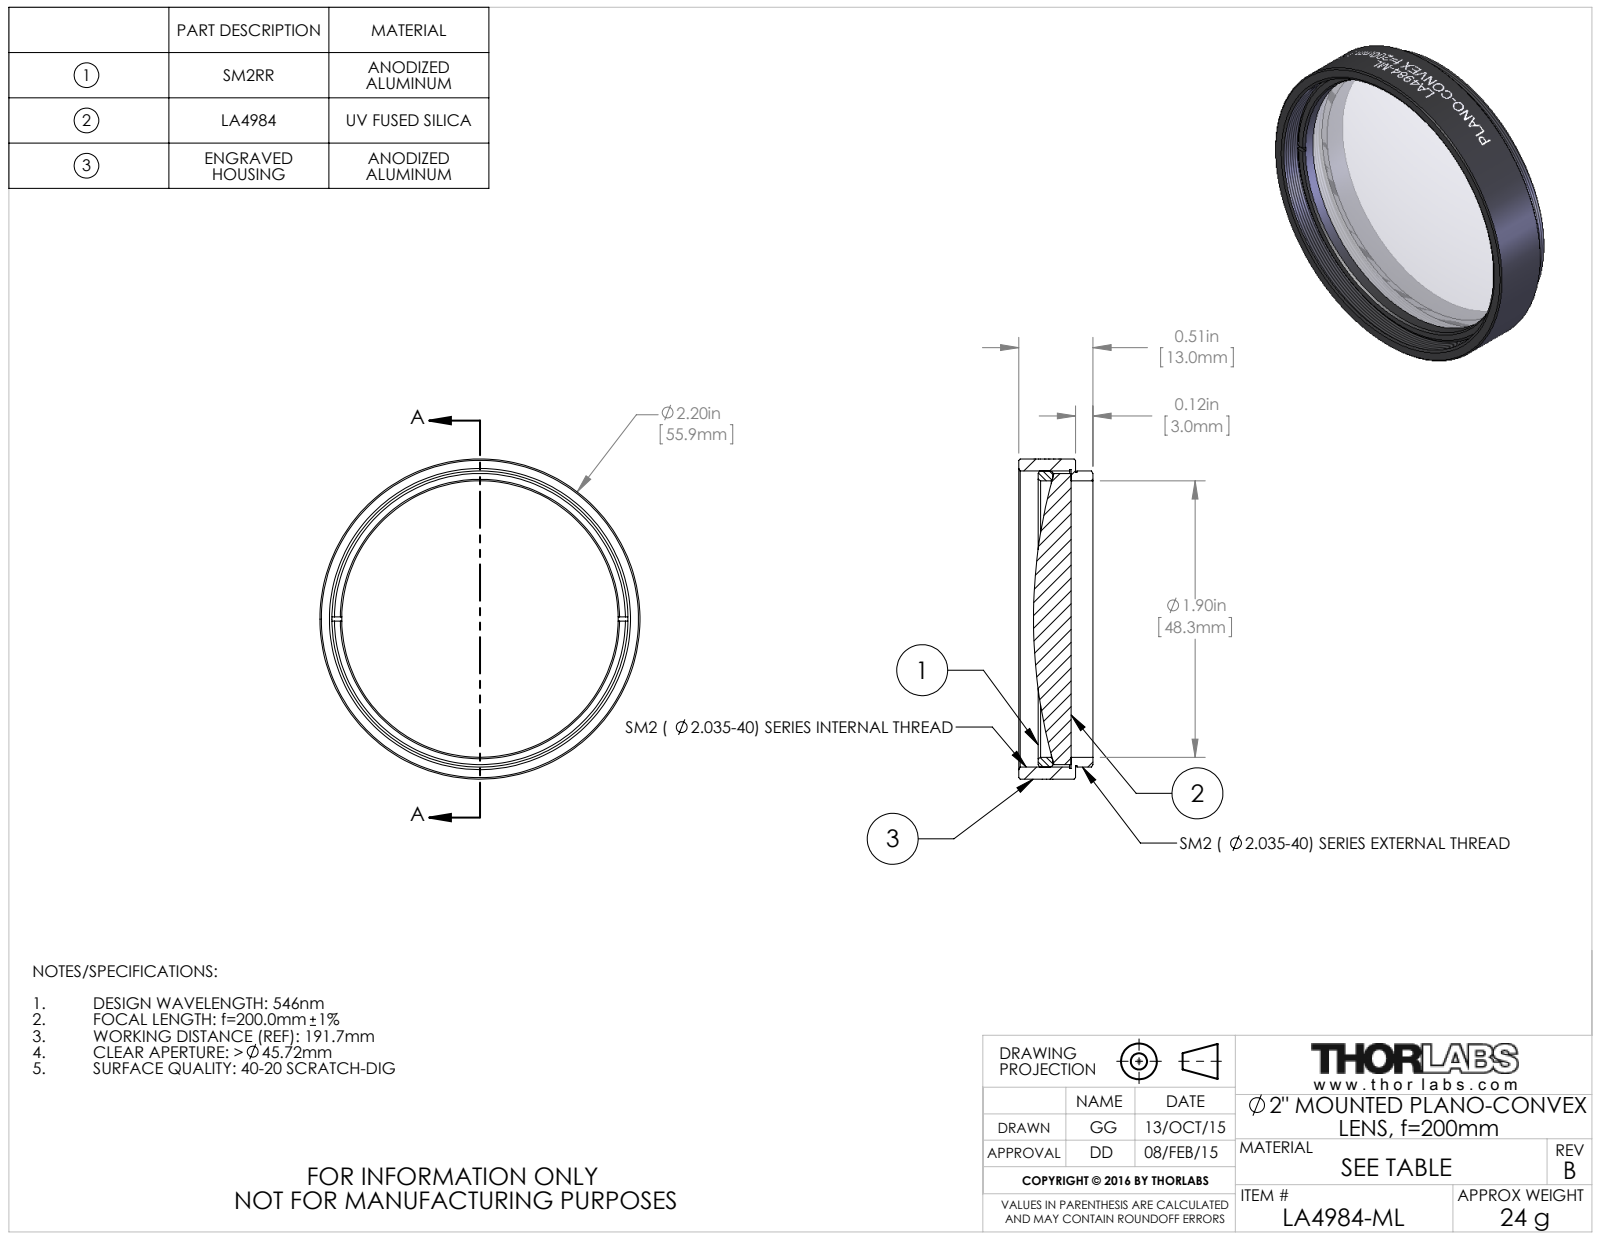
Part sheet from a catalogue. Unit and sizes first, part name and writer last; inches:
Units: inches
Overall size (bounding box): 2.2 × 2.2 × 0.51
Round holes (diameter × count): ⌀1.9 ×1, ⌀2.055 ×1
Round bosses / shafts (diameter × count): ⌀2.2 ×1, ⌀2.035 ×1, ⌀2.015 ×1, ⌀2 ×1
Main face-to-face distances: 0.03, 0.39, 0.36, 0.12, 0.15, 0.51, 0.278, 0.157, 0.128, 0.233
Volume: 0.907 in³ · Surface area: 17.65 in²
Bodies: 3 solids, 112 faces (16 planar, 76 cylindrical, 20 other)
Part name (STEP PRODUCT): TTN039461-E0W
STEP written by: SolidWorks 2014 (CONFIG_CONTROL_DESIGN)
